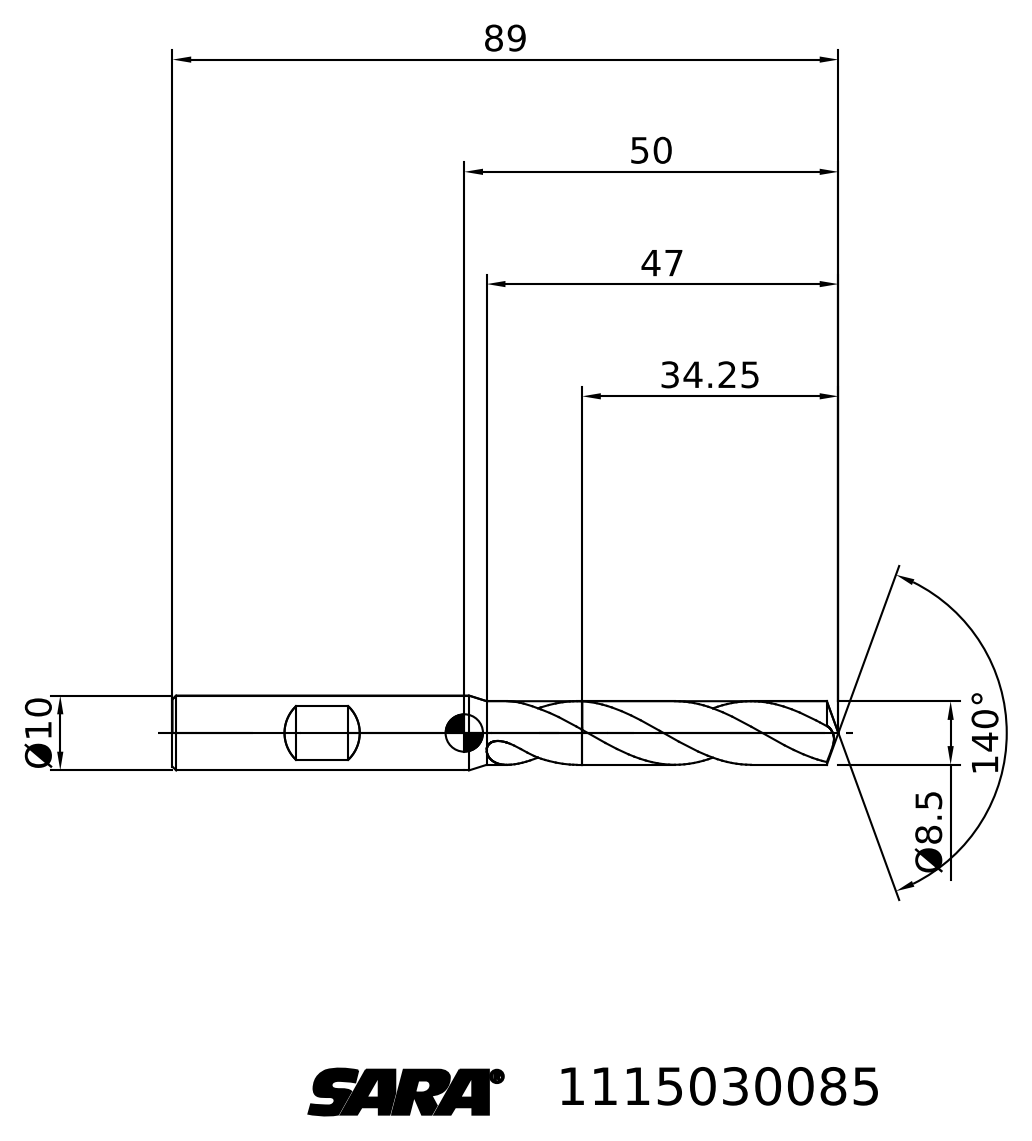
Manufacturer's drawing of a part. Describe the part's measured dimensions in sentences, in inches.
Its 3-D file was written by "TDM (AUTOMOTIVE_DESIGN)". It is 2 solids with 30 faces: 6 planar, 0 cylindrical and 24 other. Overall it measures 3.504 by 0.887 by 0.489 inches. Its volume is 0.304 cubic inches and its surface area 4.387 square inches. The main face-to-face distances are 2.156.
